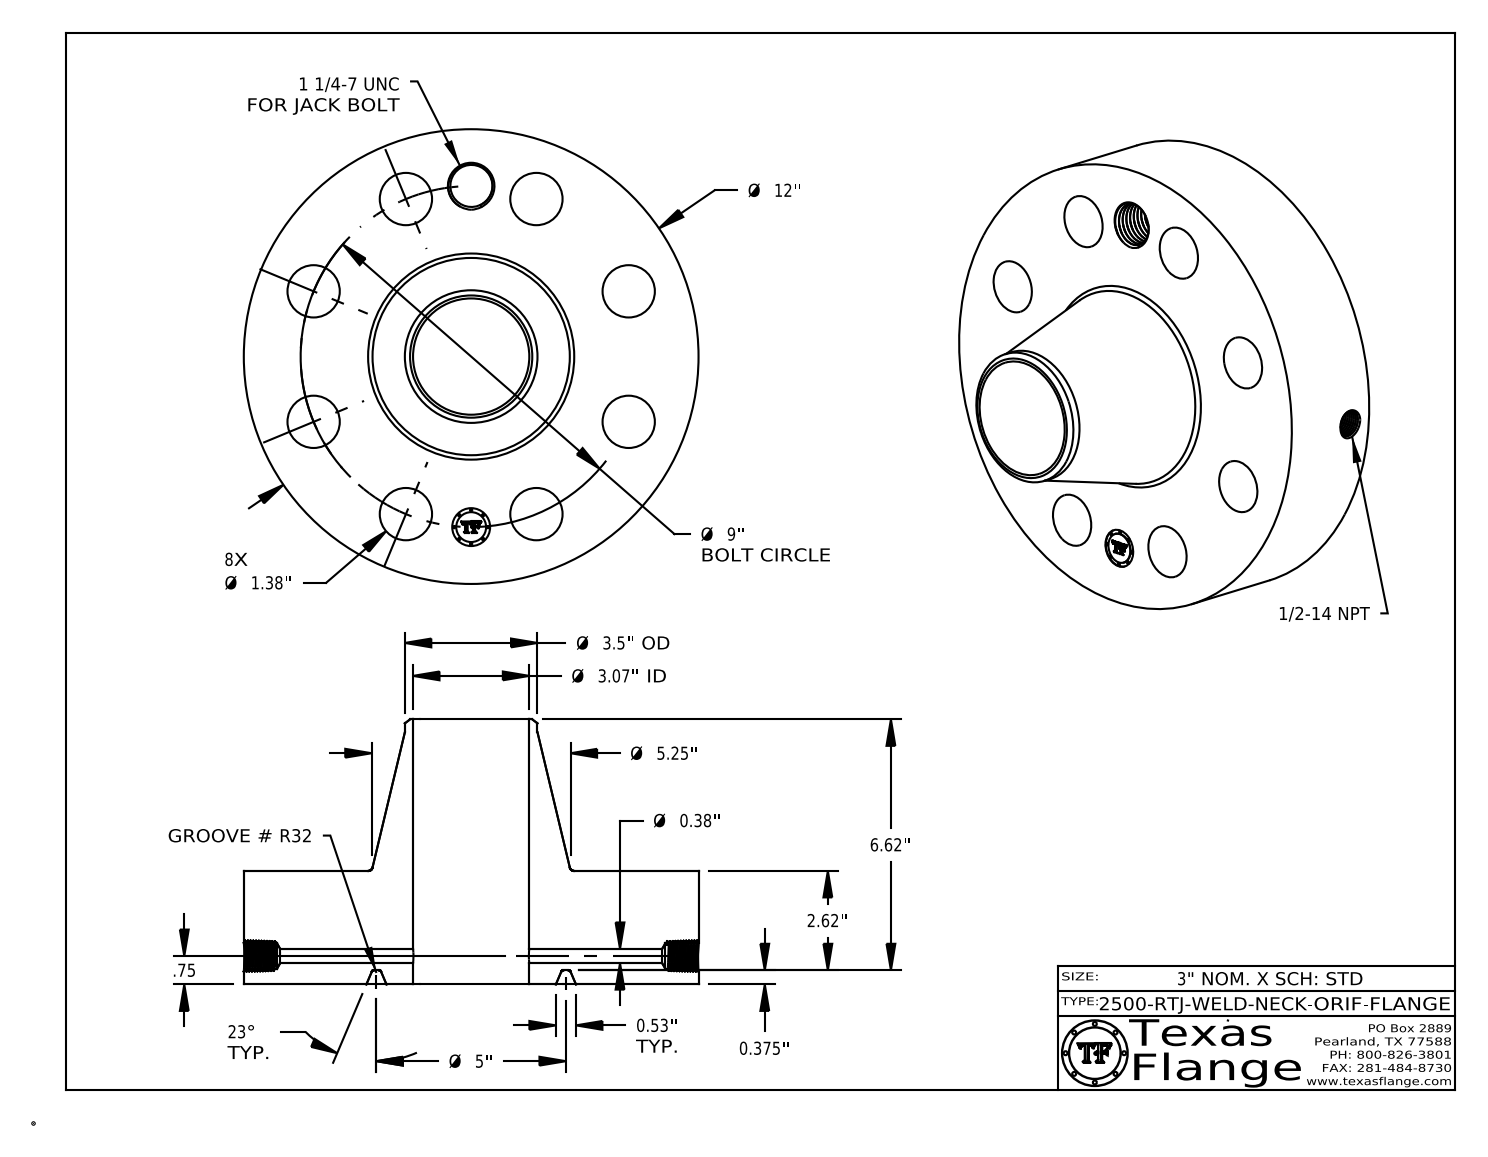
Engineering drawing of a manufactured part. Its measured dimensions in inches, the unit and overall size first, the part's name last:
Units: inches
Overall size (bounding box): 12 × 12 × 6.995
Round holes (diameter × count): ⌀1.38 ×8, ⌀0.375 ×1, ⌀0.672 ×1, ⌀1 ×1, ⌀1.109 ×1, ⌀3.068 ×1
Round bosses / shafts (diameter × count): ⌀0.061 ×8, ⌀12 ×1, ⌀3.5 ×1, ⌀0.788 ×1
Main face-to-face distances: 2.995, 0.375, 2.62, 6.995, 6.62, 4, 2.98, 2.605, 0.015, 4.015
Hole centre spacings: 4.5, 3.444, 6.364, 8.315, 9, 1.756, 5, 7.483
Volume: 303.1 in³ · Surface area: 549.7 in²
Bodies: 1 solid, 813 faces (370 planar, 103 cylindrical, 340 other)
Part name (STEP PRODUCT): 2500-RTJ-WELD-NECK
STEP written by: CATIA V5 STEP AP214 (AUTOMOTIVE_DESIGN)
